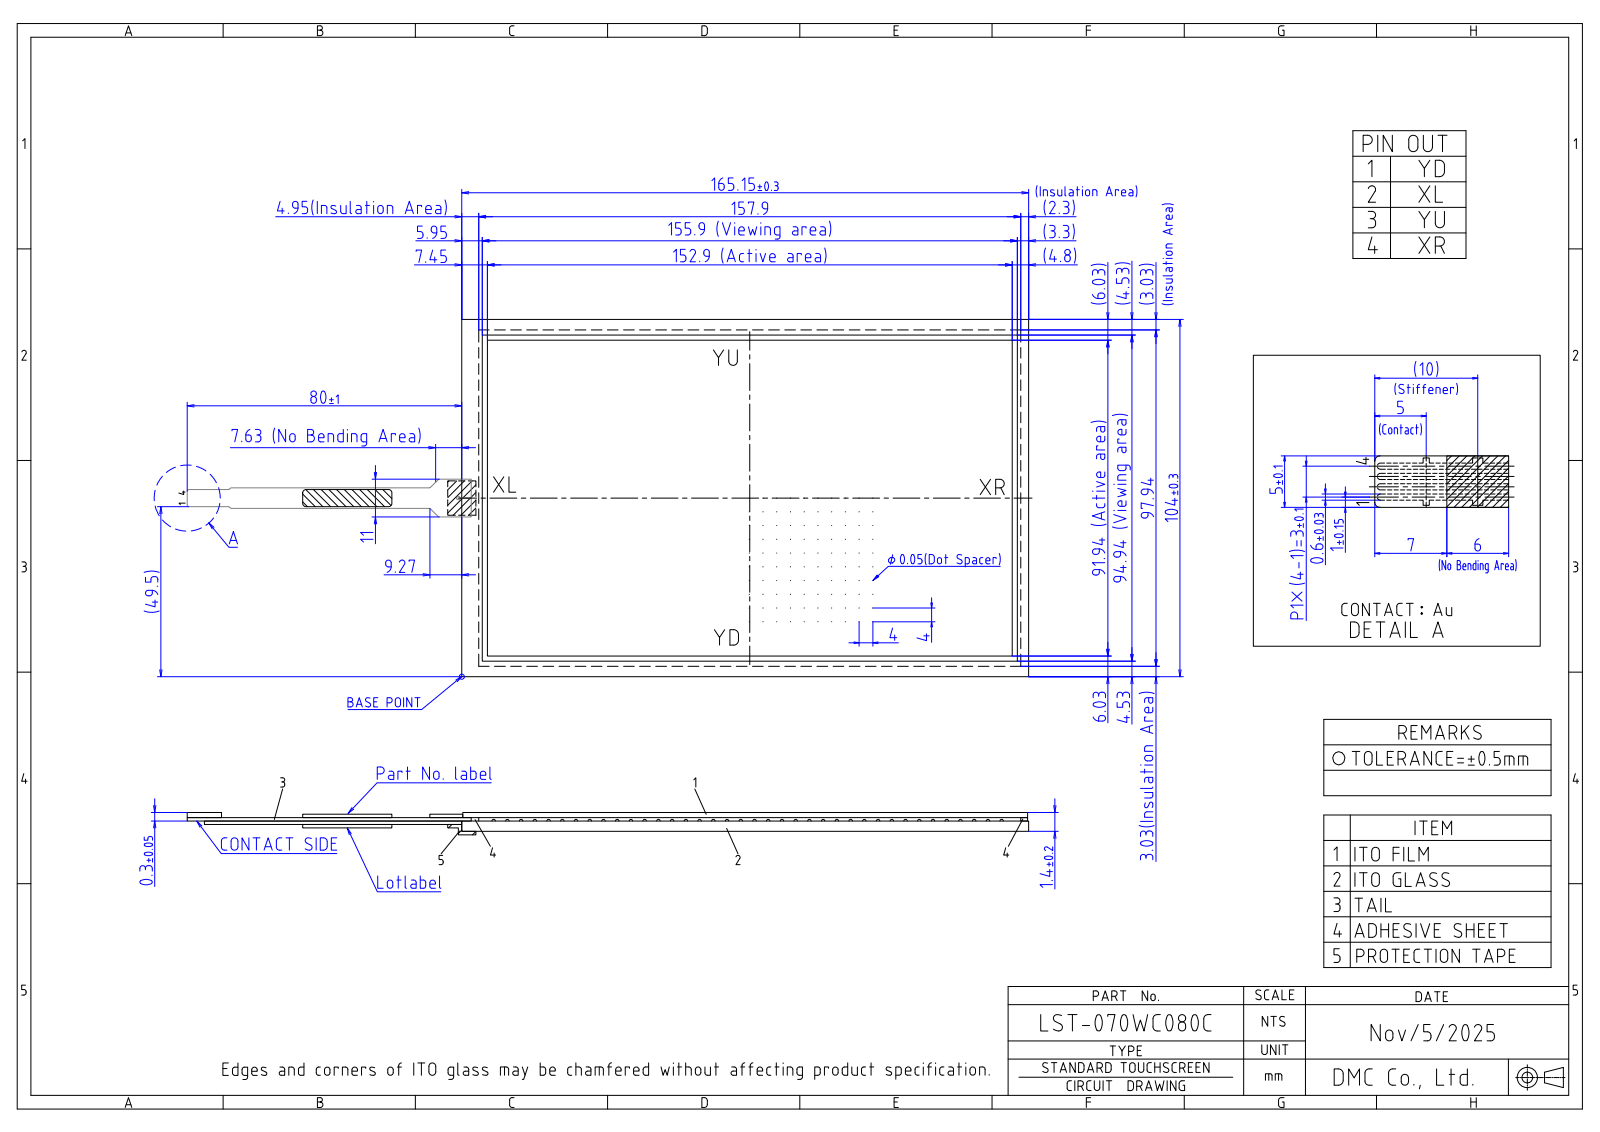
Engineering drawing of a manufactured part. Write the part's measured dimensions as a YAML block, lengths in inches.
part_name: "LST-070WC080C (3Dデータ)"
step_written_by: "Autodesk Inventor 2024 (AUTOMOTIVE_DESIGN)"
units: inches
bodies: {solids: 2, faces: 52, planar: 46, cylindrical: 6, other: 0}
overall_size: [10.952, 5.732, 0.075]
volume: 1.467
surface_area: 56.17
partial_cylinders:
  - {radius: 0.012, count: 4}
  - {radius: 0.02, count: 2}
face_to_face_distances: [0.055, 0.051, 0.059, 0.063, 4.094, 6.502, 0.02, 0.024, 0.016, 0.075]
